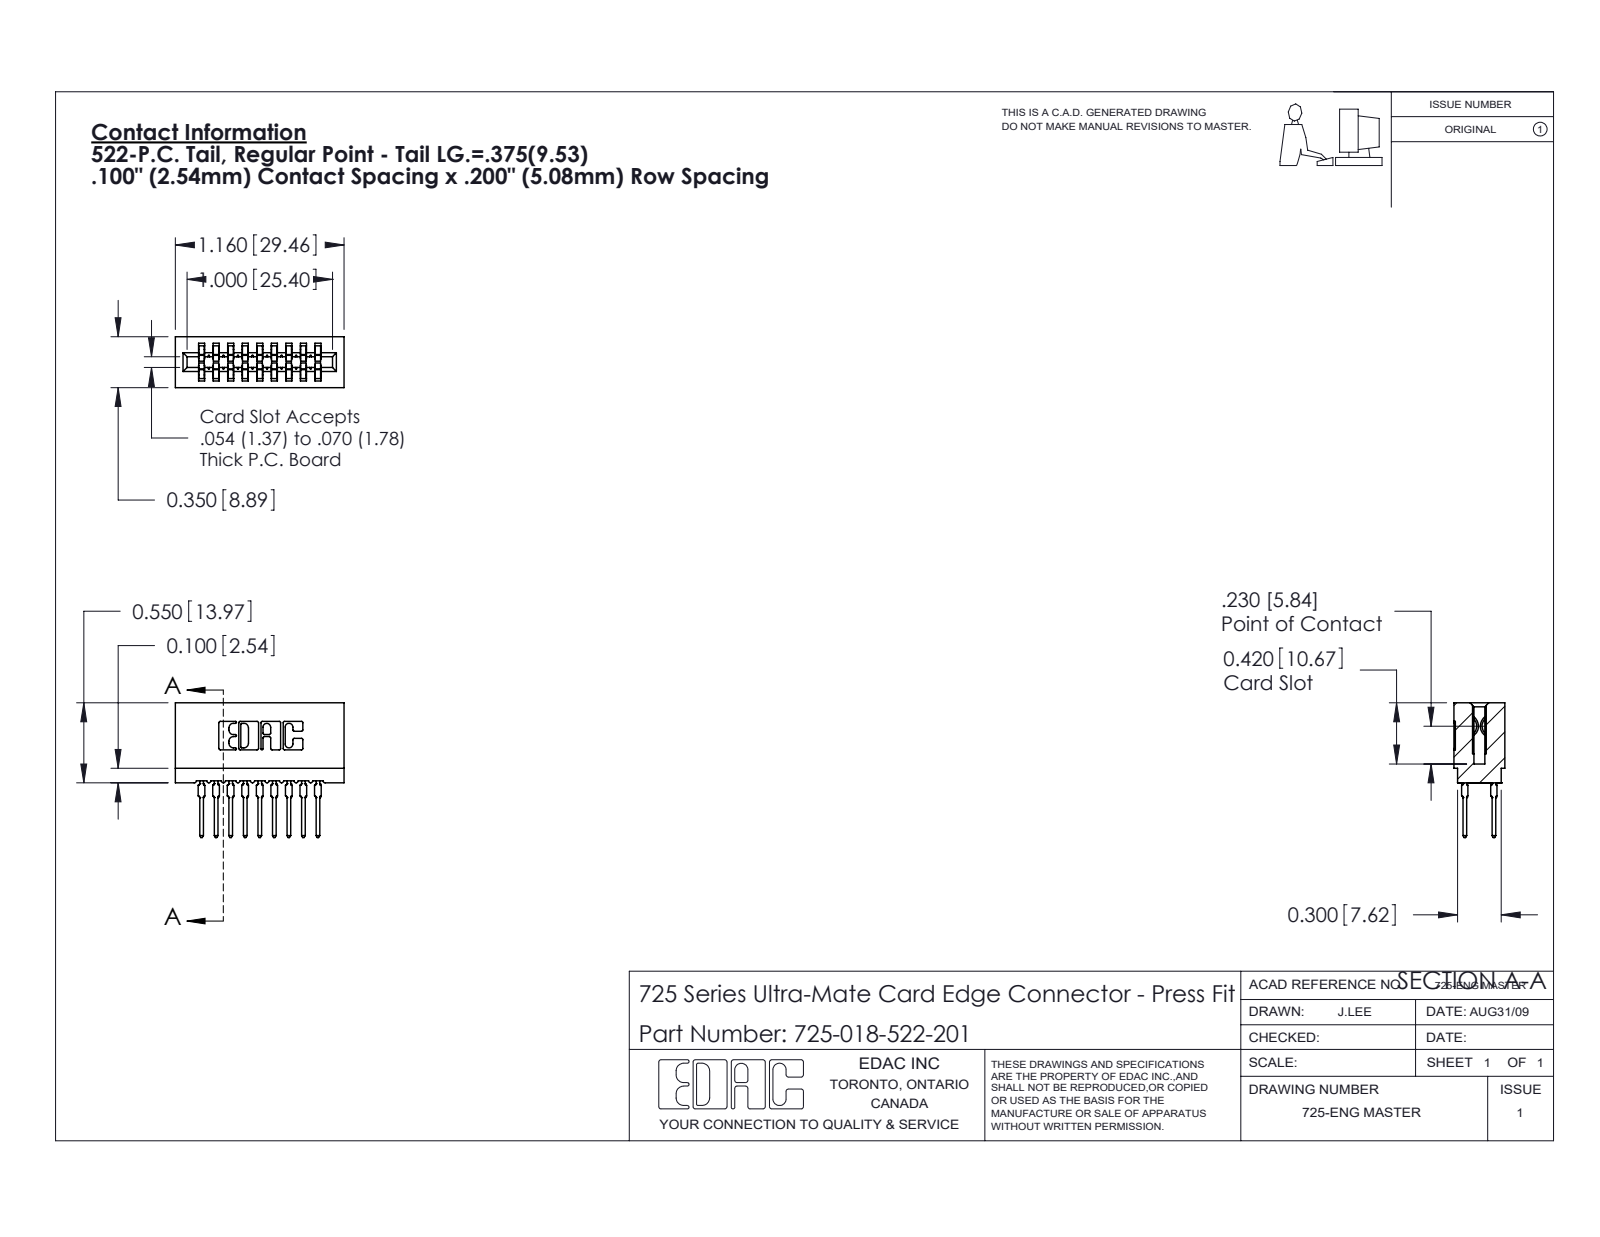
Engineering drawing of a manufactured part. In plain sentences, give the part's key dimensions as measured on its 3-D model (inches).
The part is named "725 Part_Insulator Option - 01; 745-292-001_522; 725-018-522-201". Its 3-D file was written by "SolidWorks 2020 (CONFIG_CONTROL_DESIGN)". It is 19 solids with 1706 faces: 883 planar, 355 cylindrical and 468 other. Overall it measures 1.16 by 0.926 by 0.35 inches. Its volume is 0.154 cubic inches and its surface area 7.265 square inches. Partial cylindrical surfaces (rounded edges, fillets, slot ends): 36 of radius 0.021, 22 of radius 0.01, 18 of radius 0.015, 8 of radius 0.005, 8 of radius 0.011, 6 of radius 0.007, 6 of radius 0.031, 3 of radius 0.026. The main face-to-face distances are 0.2, 0.1, 0.3, 0.4, 0.042, 0.5, 0.142, 0.058, 0.242, 0.158.
